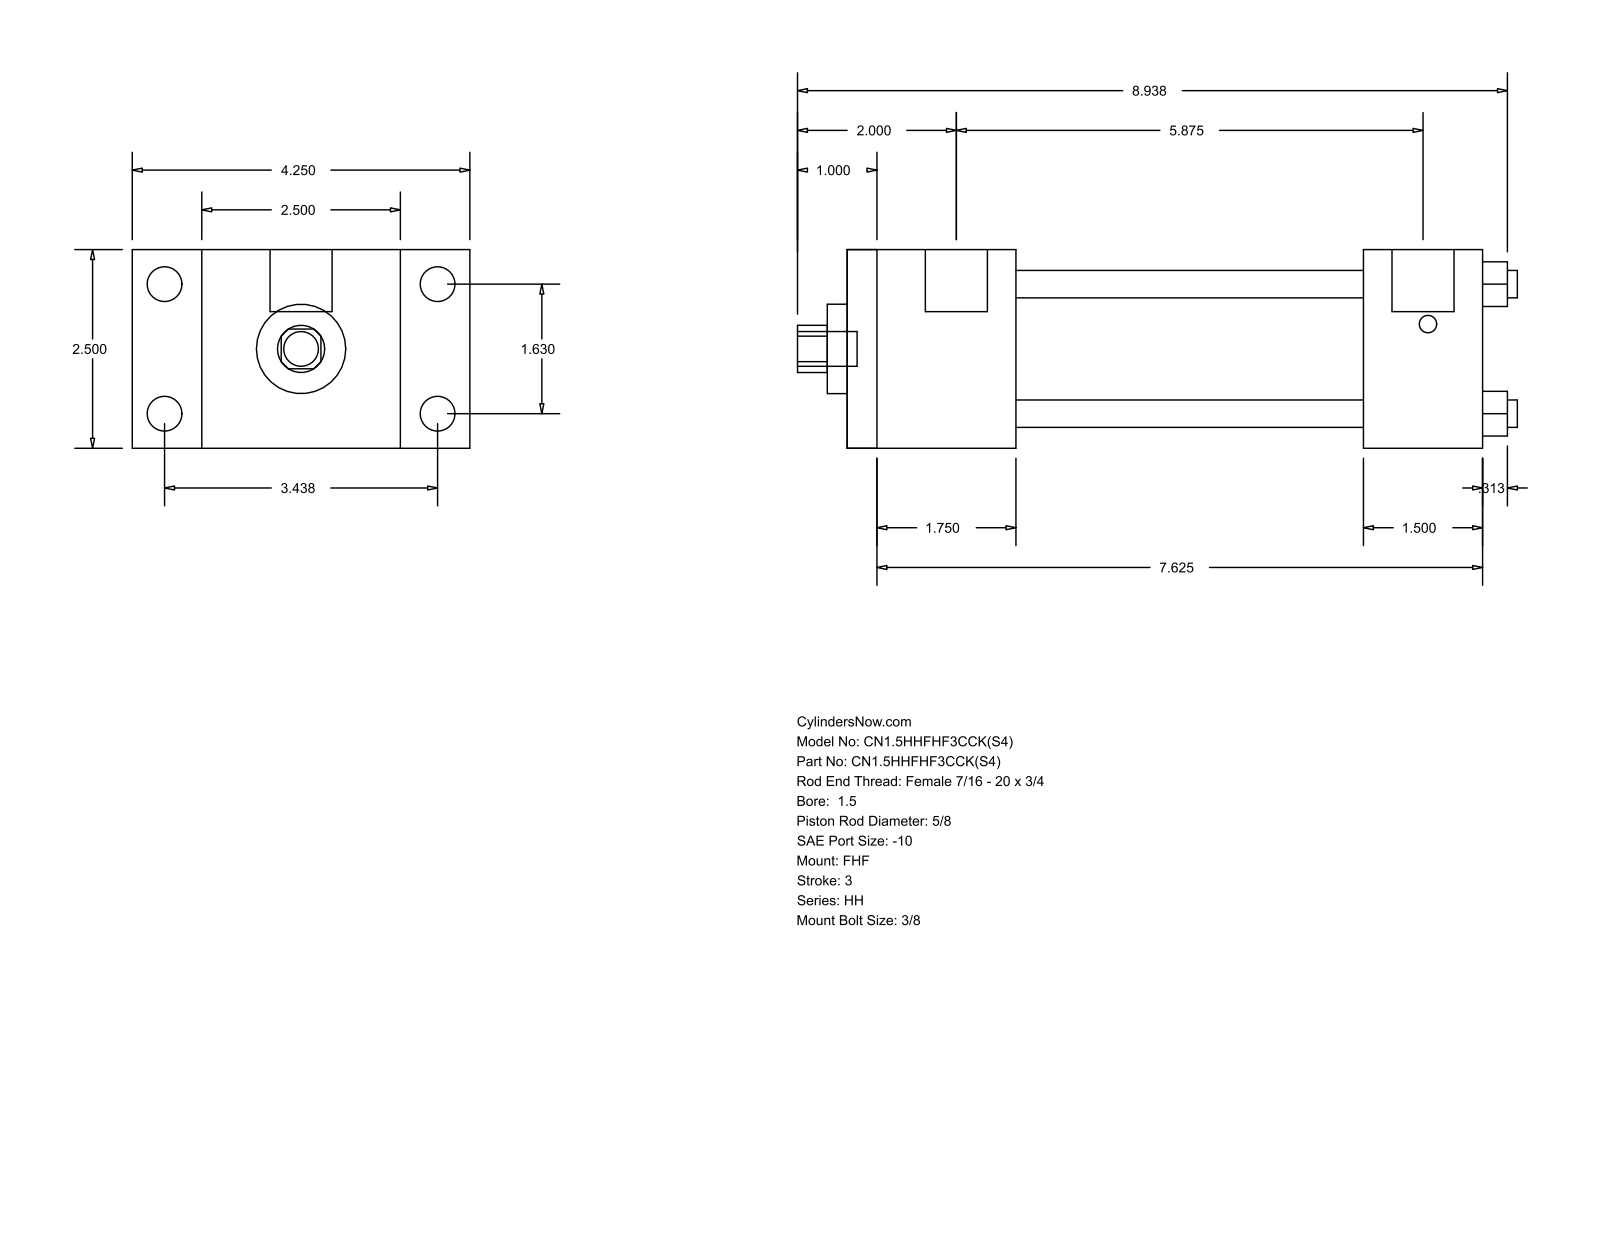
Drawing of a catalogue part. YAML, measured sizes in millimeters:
part_name: "HH_FHF__0150_0.625"
step_written_by: "GSSL Pune (CONFIG_CONTROL_DESIGN)"
units: millimeters
bodies: {solids: 0, faces: 88, planar: 60, cylindrical: 28, other: 0}
overall_size: [230.19, 107.95, 63.5]
round_holes:
  - {diameter: 8.76, count: 4}
  - {diameter: 15.88, count: 1}
  - {diameter: 28.57, count: 1}
  - {diameter: 44.45, count: 1}
round_bosses_or_shafts:
  - {diameter: 11.13, count: 4}
  - {diameter: 5.56, count: 4}
  - {diameter: 19.84, count: 2}
  - {diameter: 11.11, count: 1}
partial_cylinders:
  - {radius: 7.54, count: 1}
face_to_face_distances: [63.5, 22.23, 85.73, 53.97, 107.96, 203.19, 149.22, 38.1, 165.09, 111.12]
hole_center_spacings: [29.27, 41.4, 58.55]
